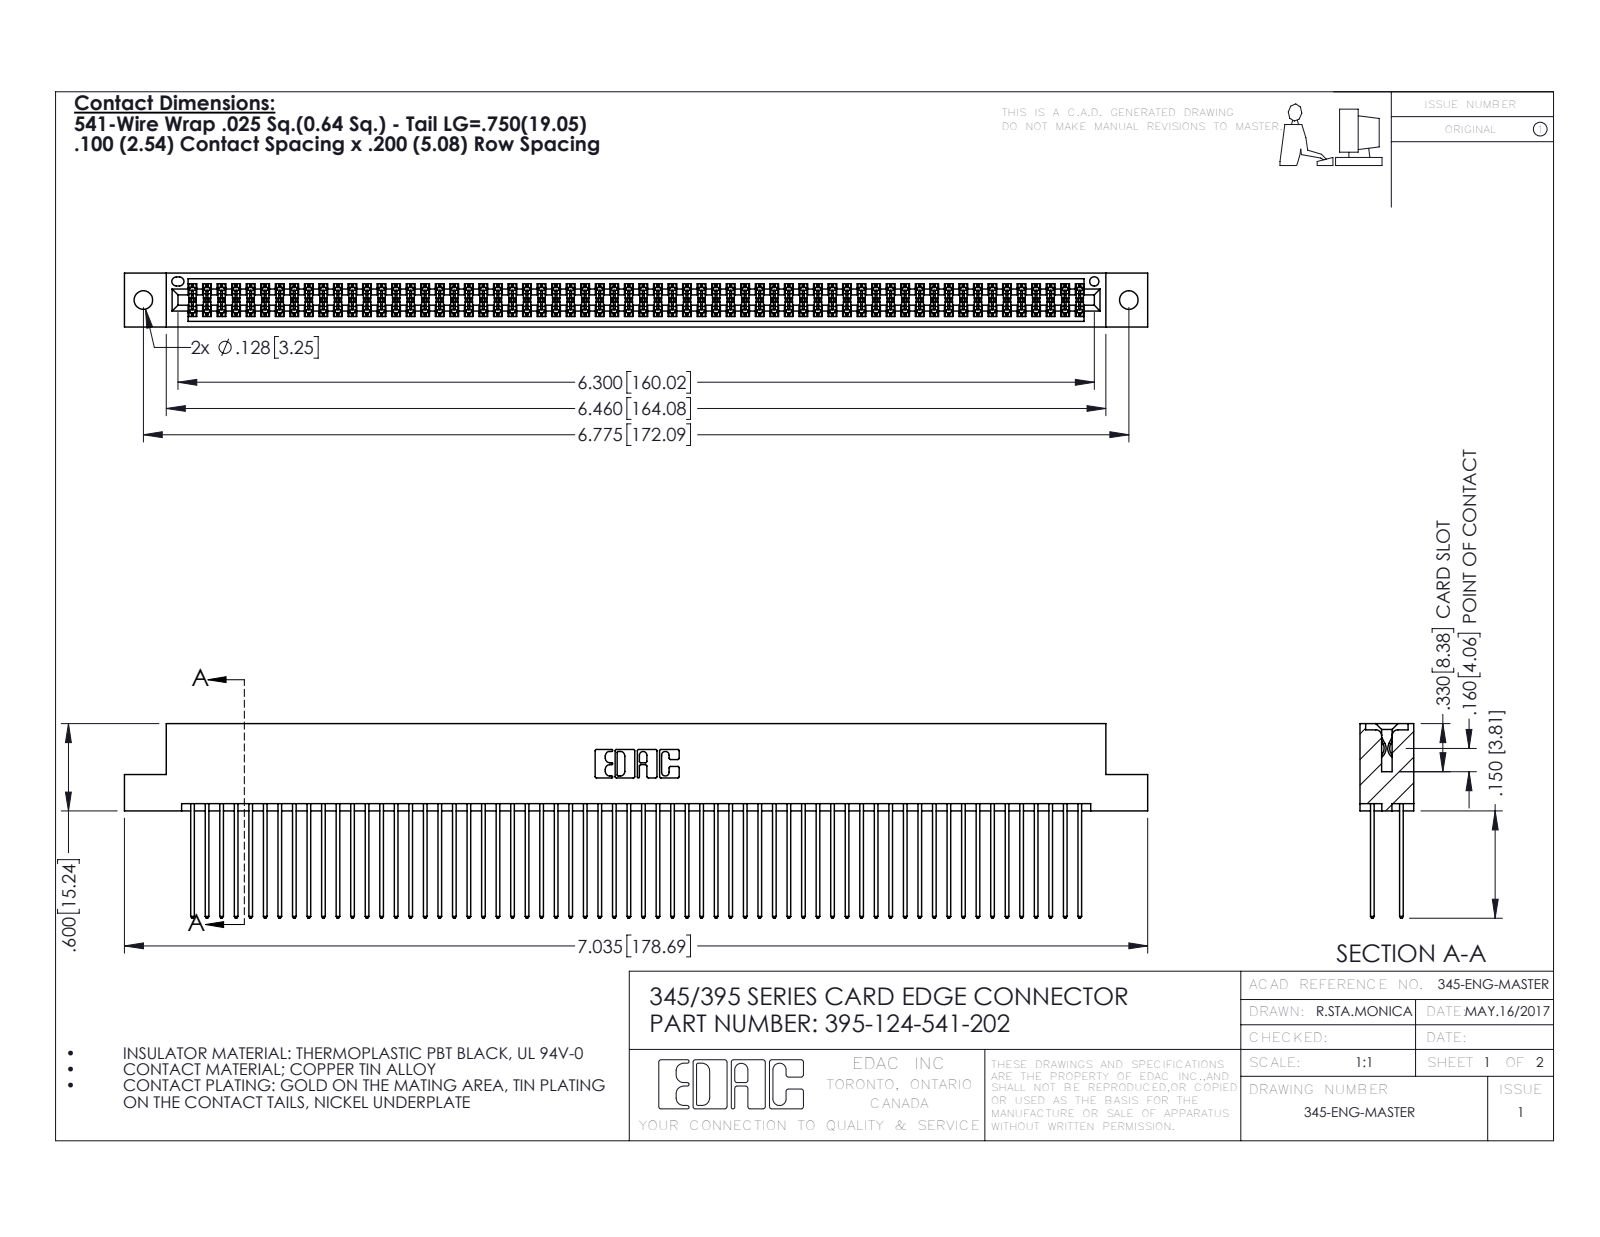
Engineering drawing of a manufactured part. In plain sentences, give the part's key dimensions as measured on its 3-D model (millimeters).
The part is named "395-124-541-202; 345-292-001_345-293-141; 345 Part_Flush Mounting Lugs - 0.128 Dia". Its 3-D file was written by "SolidWorks 2016 (CONFIG_CONTROL_DESIGN)". It is 125 solids with 6326 faces: 4172 planar, 2154 cylindrical and 0 other. Overall it measures 178.7 by 34 by 9.4 millimeters. Its volume is 18 220 cubic millimeters and its surface area 30 390 square millimeters. Round holes: 2 of diameter 3.3, 1 of diameter 1.6. Partial cylindrical surfaces (rounded edges, fillets, slot ends): 186 of radius 0.2, 124 of radius 0.3, 22 of radius 0.3, 6 of radius 0.2, 6 of radius 0.8, 3 of radius 0.7, 2 of radius 0.4, 2 of radius 0.5. The main face-to-face distances are 7.6, 1.8, 5.1, 2.5, 6.9, 0.6, 5.7, 9.4, 4.4, 3.8. The hole center spacings are 6.9, 166.1, 172.1.
